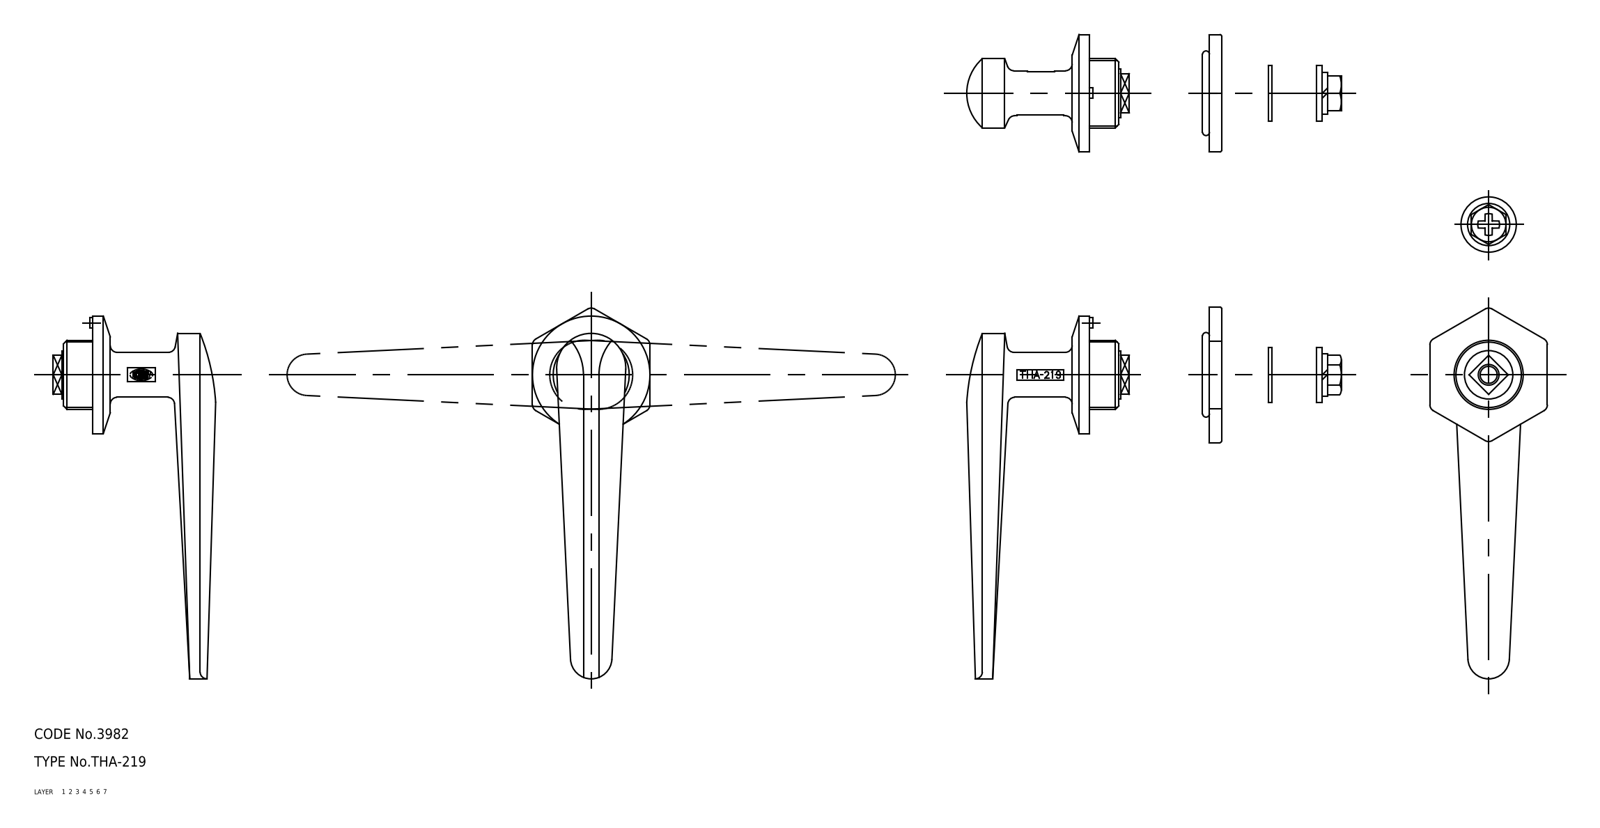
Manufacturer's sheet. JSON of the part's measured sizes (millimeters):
{"part_name": "handle; washer_C; washer_B; washer_A (+4 more)", "step_written_by": "CADfix (AUTOMOTIVE_DESIGN)", "units": "millimeters", "bodies": {"solids": 7, "faces": 155, "planar": 0, "cylindrical": 0, "other": 155}, "overall_size": [107.32, 54.1, 34], "volume_mm3": 22551, "surface_area_mm2": 13493}
